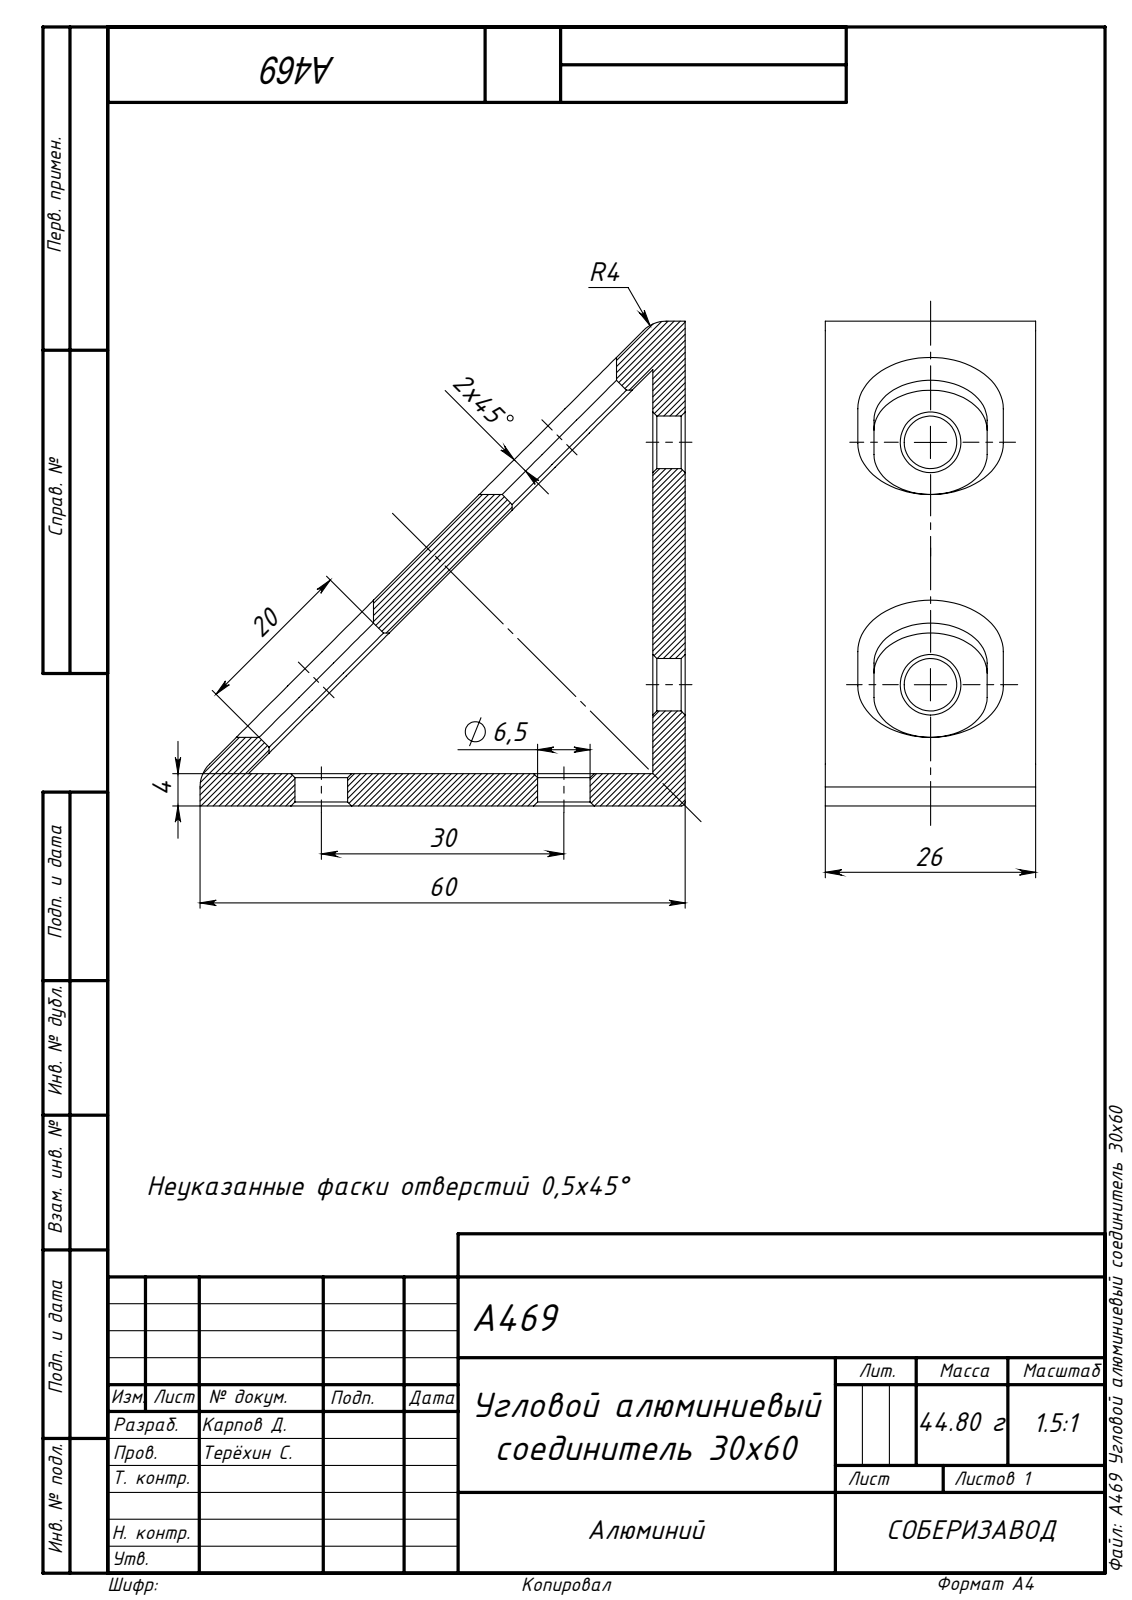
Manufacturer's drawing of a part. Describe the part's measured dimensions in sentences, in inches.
The part is named "A469 Угловой алюминиевый соединитель 30х60". Its 3-D file was written by "SolidWorks 2021 (AUTOMOTIVE_DESIGN)". It is 1 solid with 67 faces: 22 planar, 17 cylindrical and 28 other. Overall it measures 2.362 by 2.362 by 1.024 inches. Its volume is 1.067 cubic inches and its surface area 16.68 square inches. Round holes: 4 of diameter 0.256. Partial cylindrical surfaces (rounded edges, fillets, slot ends): 4 of radius 0.276, 2 of radius 0.157, 1 of radius 0.02. The main face-to-face distances are 0.157, 0.167, 1.024, 2.362, 2.205, 0.236, 0.787, 0.551, 0.341. The hole center spacings are 1.181.
